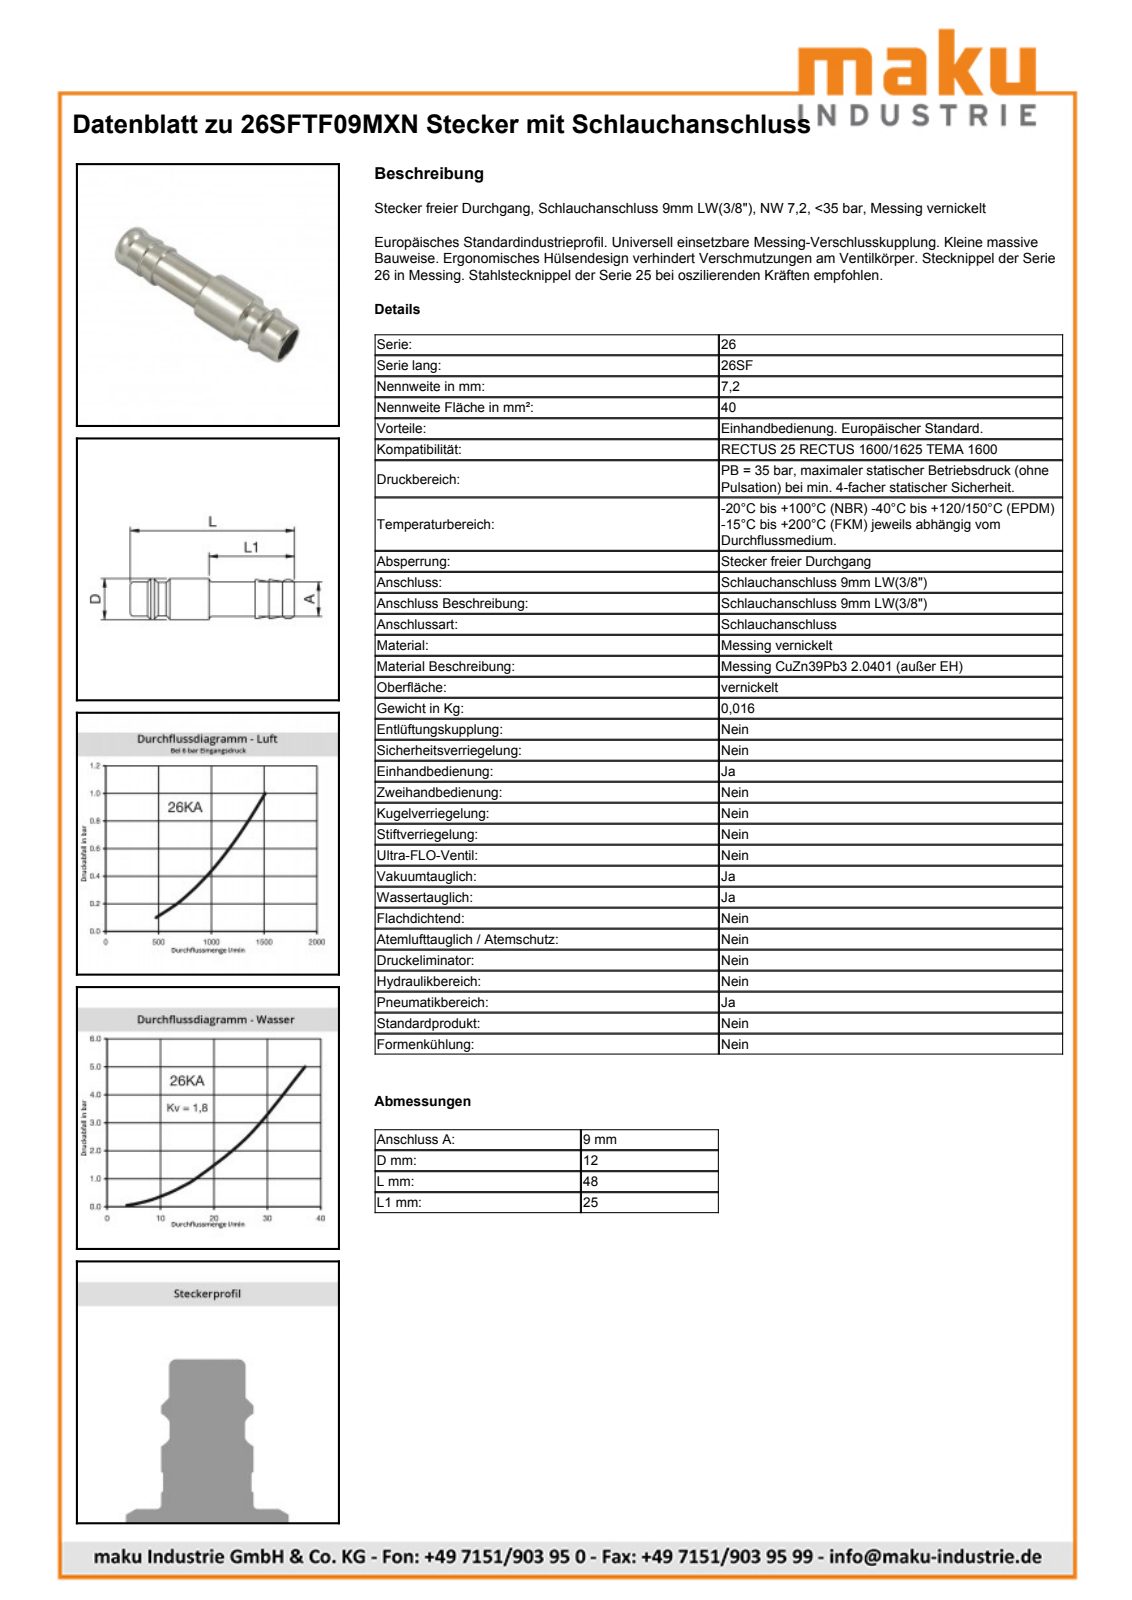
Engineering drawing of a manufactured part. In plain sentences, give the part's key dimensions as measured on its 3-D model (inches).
The part is named "D106812". Its 3-D file was written by "Autodesk Inventor 2013 (AUTOMOTIVE_DESIGN)". It is 1 solid with 23 faces: 4 planar, 7 cylindrical and 12 other. Overall it measures 1.89 by 0.472 by 0.472 inches. Its volume is 0.121 cubic inches and its surface area 4.383 square inches. Round holes: 1 of diameter 0.276, 1 of diameter 0.309. Round bosses or shafts: 1 of diameter 0.472, 1 of diameter 0.394, 1 of diameter 0.384, 1 of diameter 0.358. The main face-to-face distances are 0.984, 0.531, 0.453, 0.906, 1.437, 1.89.
